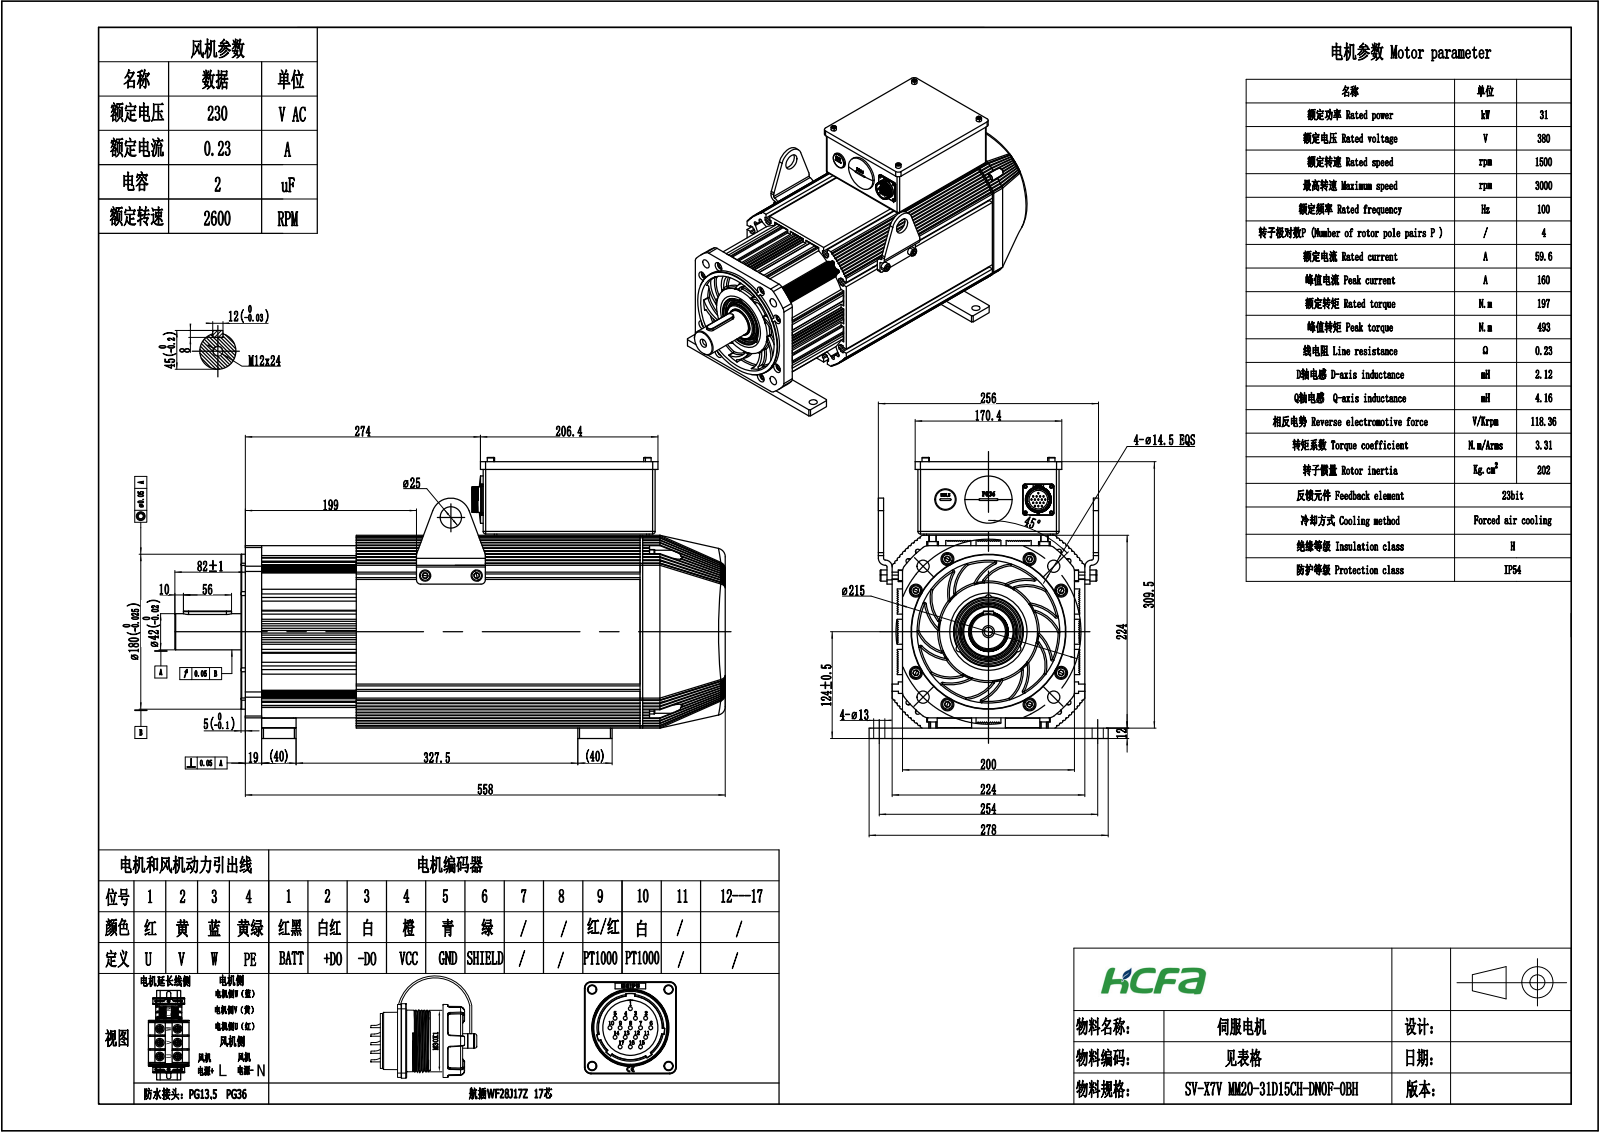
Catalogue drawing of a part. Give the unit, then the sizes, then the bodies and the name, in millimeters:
Units: millimetres
Overall size (bounding box): 640 × 326.5 × 278
Round holes (diameter × count): ⌀9 ×22, ⌀15 ×14, ⌀13 ×8, ⌀2.5 ×4, ⌀5 ×4, ⌀6.8 ×4, ⌀7 ×4, ⌀10 ×4, ⌀14.5 ×4, ⌀10.2 ×1, ⌀20.5 ×1, ⌀21.7 ×1
Round bosses / shafts (diameter × count): ⌀8 ×20, ⌀1.5 ×17, ⌀13 ×16, ⌀10 ×4, ⌀8.5 ×4, ⌀6 ×4, ⌀40 ×2, ⌀180 ×1
Partial cylindrical surfaces — rounded edges, fillets, slot ends (radius × count): R2 ×112, R1 ×22, R1.5 ×20, R5 ×18, R1.4 ×16, R3 ×12, R0.2 ×10, R10 ×10
Main face-to-face distances: 224, 2, 307.5, 12, 6, 83.5, 212, 309.5, 85.5, 30
Hole centre spacings: 29.47, 43.17, 97, 124.07, 137.18, 138.41, 162.9, 167.15
Volume: 23 890 000 mm³ · Surface area: 1 177 000 mm²
Bodies: 7 solids, 3585 faces (1524 planar, 1134 cylindrical, 927 other)
Part name (STEP PRODUCT): 10002030101-0041-SV-X7VMM20-31D15CH-DN0F-0BH-9段外形图
STEP written by: SolidWorks 2021 (CONFIG_CONTROL_DESIGN)
